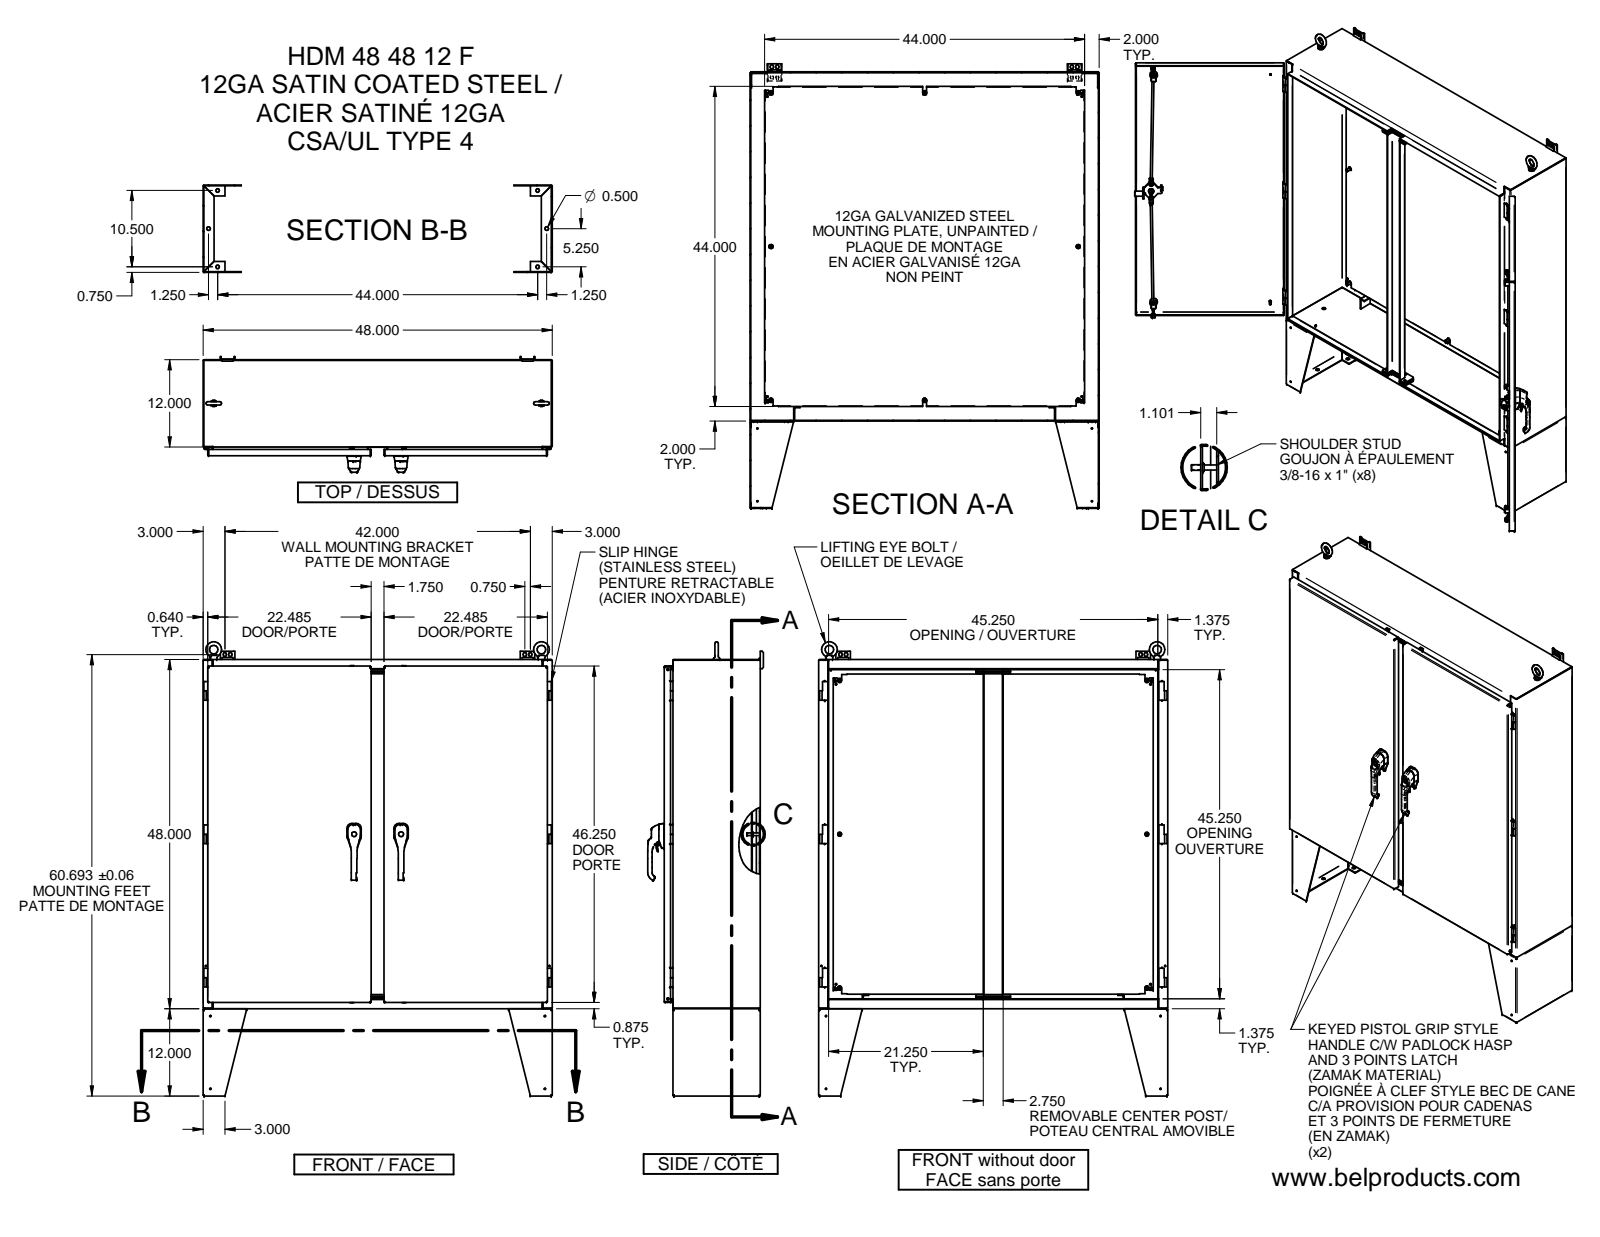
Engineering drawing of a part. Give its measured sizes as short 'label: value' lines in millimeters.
name: HDM484812F_12GA_AHDN; HDM484812F_12GA_4_U; HD484812U_12GA; HDFXX4812B_12GA_4 (+8 more)
written by: Solid Edge (AUTOMOTIVE_DESIGN)
unit: mm
bodies: 95 solids, 6574 faces (3170 planar, 1638 cylindrical, 1766 other)
size: 1586.2 × 1219.2 × 403.76
volume: 18 210 000 mm³; area: 13 610 000 mm²
holes: 22× ⌀3.16, 18× ⌀3.17, 16× ⌀12.7, 8× ⌀5.11, 6× ⌀5.4, 5× ⌀4.19, 4× ⌀0.35, 4× ⌀2.69, 4× ⌀4.06, 4× ⌀4.3, 4× ⌀5, 4× ⌀5.23
bosses: 22× ⌀3.17, 18× ⌀3.02, 8× ⌀16.19, 8× ⌀9.53, 8× ⌀8.97, 8× ⌀7.62, 8× ⌀0.79, 6× ⌀28
rounds: 297× R0.5, 98× R0.3, 48× R3, 41× R0.47, 39× R0.81, 33× R3.48, 27× R2, 25× R1.59
face distances: 2.67, 2.66, 304.95, 1216.53, 332.91, 335.58, 330.25, 332.92, 307.61, 25.3
hole spacings: 500.66, 68.66, 536.58, 1199.83, 1279.89, 432, 1001.32, 569.32
